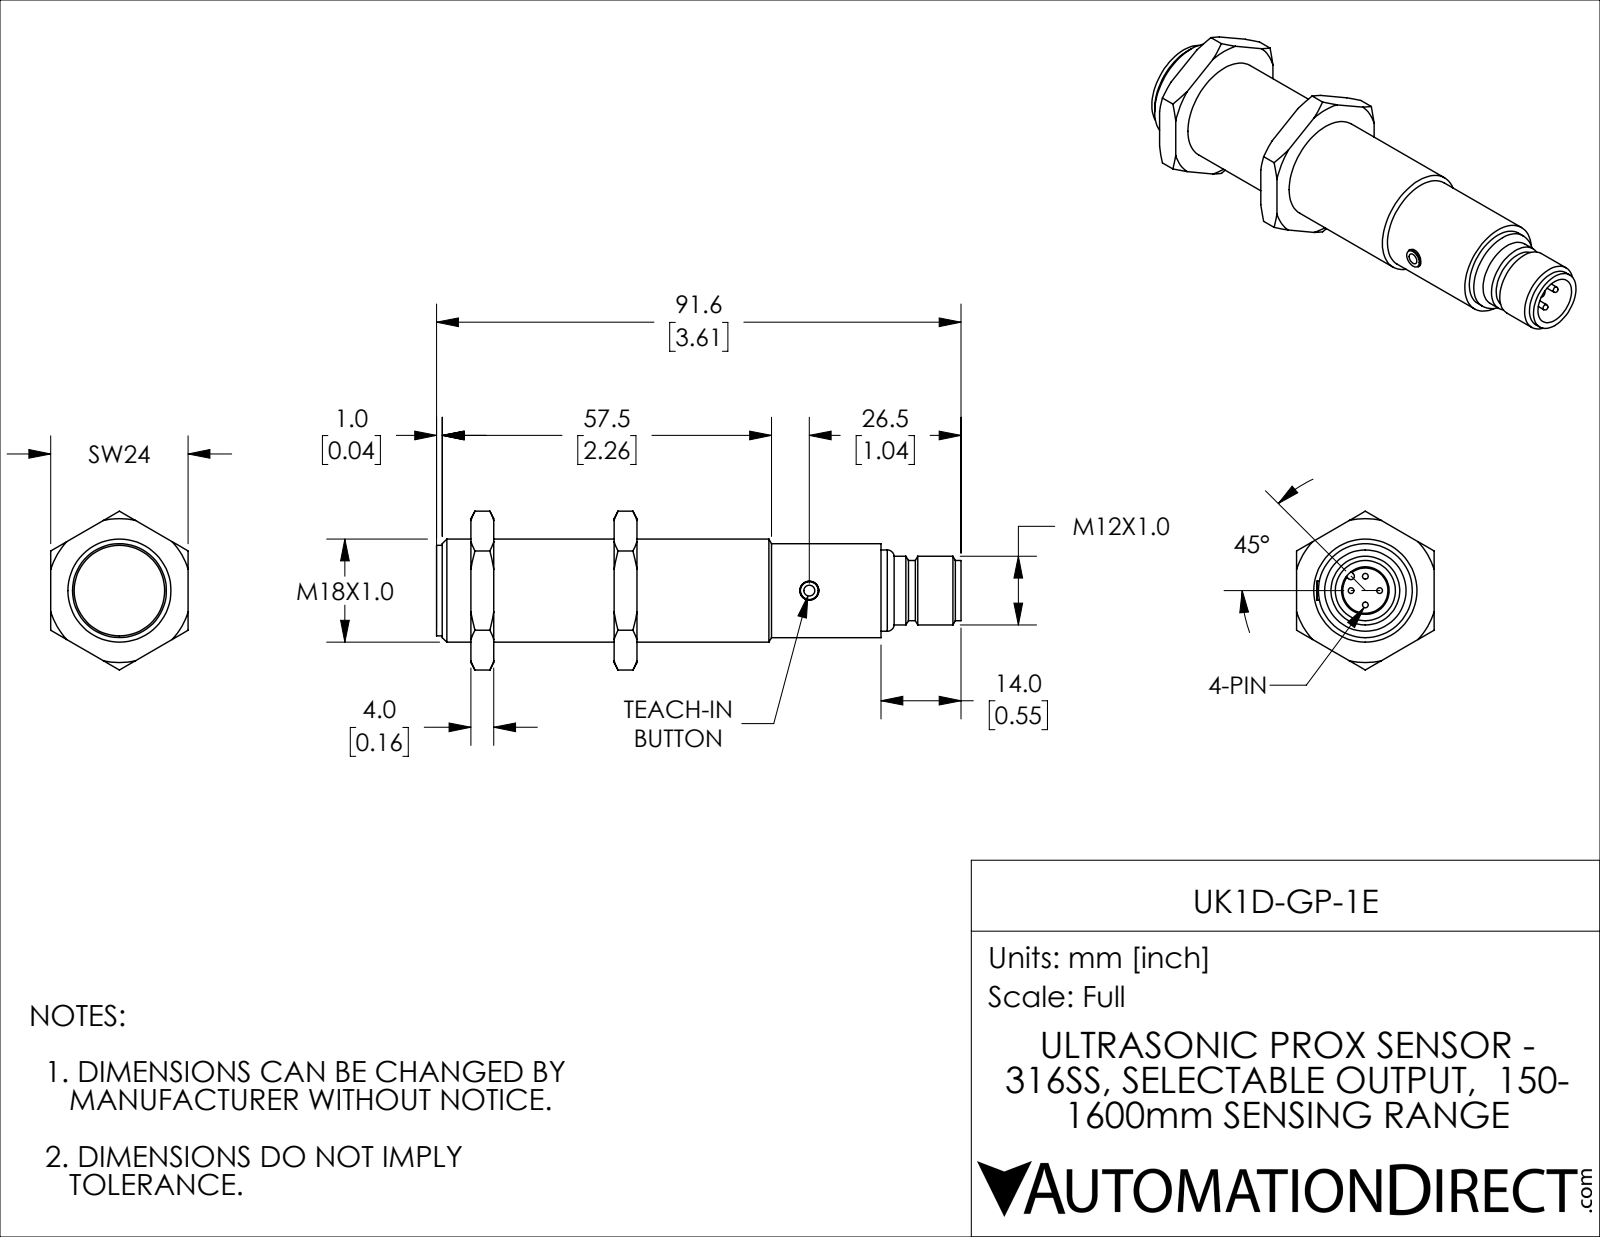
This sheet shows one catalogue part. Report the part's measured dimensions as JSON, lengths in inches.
{"part_name": "UK1D-GP-1E", "step_written_by": "SolidWorks 2018 (AUTOMOTIVE_DESIGN)", "units": "inches", "bodies": {"solids": 4, "faces": 113, "planar": 27, "cylindrical": 35, "other": 51}, "overall_size": [3.606, 1.091, 0.945], "volume_in3": 1.338, "surface_area_in2": 11.97, "round_holes": [[0.13, 1], [0.327, 1], [0.709, 1]], "round_bosses_or_shafts": [[0.039, 4], [0.646, 1], [0.622, 1], [0.559, 1], [0.472, 1], [0.413, 1]], "partial_cylinders_radius": [[0.024, 1]], "face_to_face_distances": [0.984, 0.157, 0.945, 1.142, 0.827, 0.236, 0.394, 1.22, 1.378, 3.055]}
